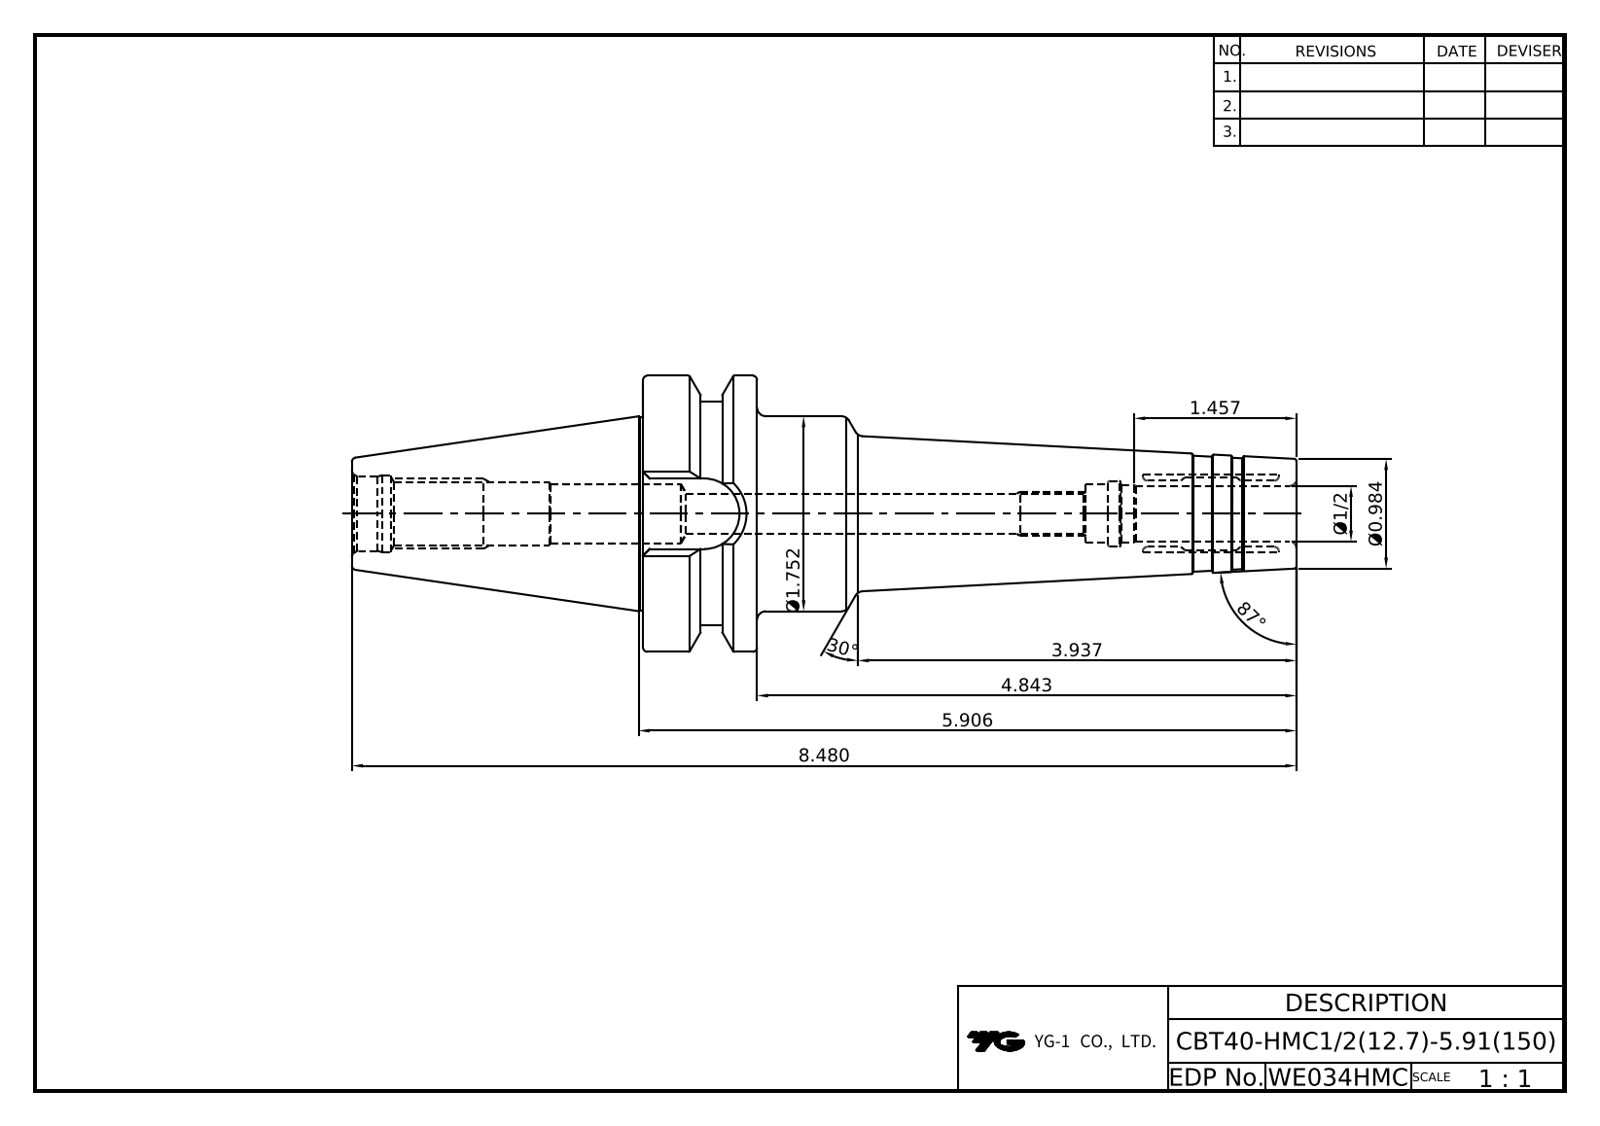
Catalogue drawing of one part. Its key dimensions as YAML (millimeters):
part_name: "LO-CBT40-HMC12.7-150"
step_written_by: "Autodesk Inventor 2022 (AUTOMOTIVE_DESIGN)"
units: millimeters
bodies: {solids: 1, faces: 81, planar: 24, cylindrical: 16, other: 41}
overall_size: [215.4, 63, 63]
volume: 223232
surface_area: 38734
round_holes:
  - {diameter: 8.92, count: 1}
  - {diameter: 12.7, count: 1}
  - {diameter: 13.3, count: 1}
  - {diameter: 13.5, count: 1}
  - {diameter: 13.84, count: 1}
  - {diameter: 17, count: 1}
  - {diameter: 17.6, count: 1}
round_bosses_or_shafts:
  - {diameter: 63, count: 1}
  - {diameter: 51, count: 1}
  - {diameter: 44.5, count: 1}
  - {diameter: 44, count: 1}
partial_cylinders:
  - {radius: 8.05, count: 1}
face_to_face_distances: [26, 149, 123, 45.2, 5, 18.1, 7.9, 130.9, 13.1, 12.9]
